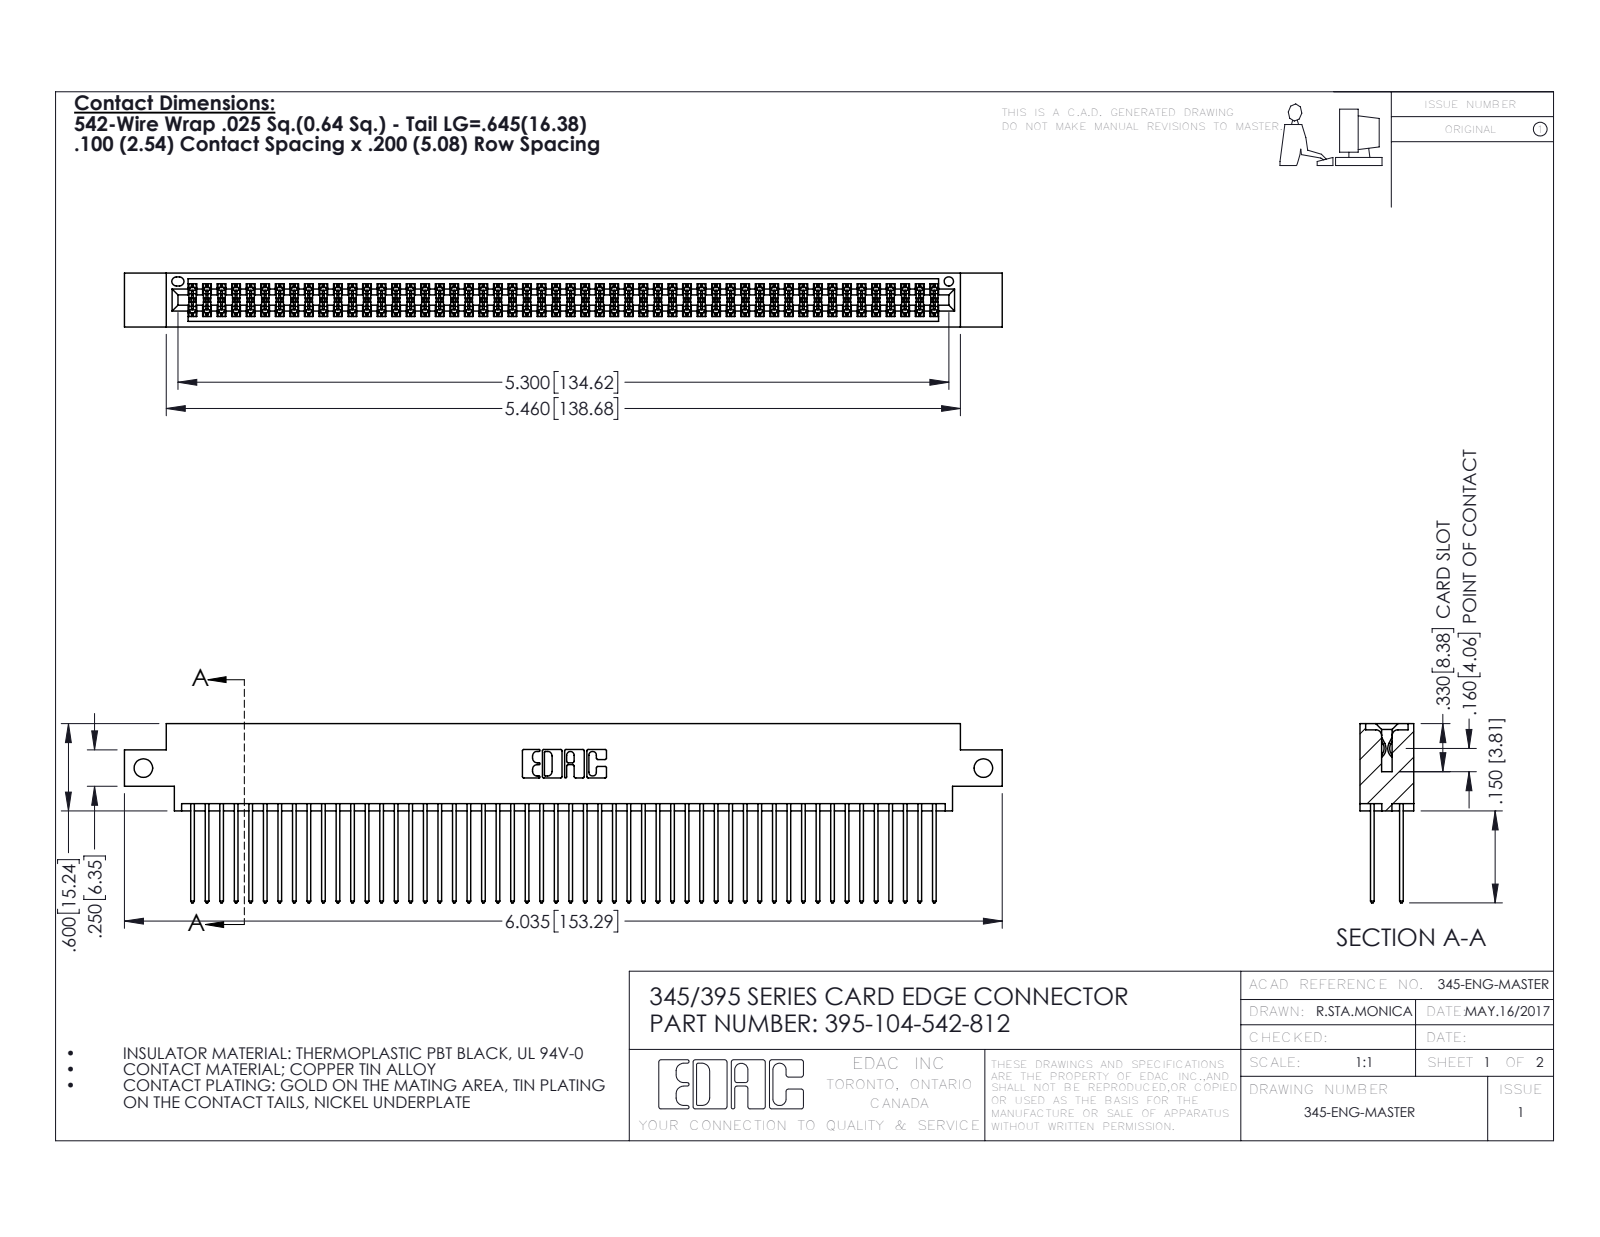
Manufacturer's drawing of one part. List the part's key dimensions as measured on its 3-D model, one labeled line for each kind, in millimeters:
Part name (STEP PRODUCT): 395-104-542-812; 345-292-001_345-293-142; 345 Part_0.170 Offset - Side Mount
STEP written by: SolidWorks 2016 (CONFIG_CONTROL_DESIGN)
Units: millimetres
Bodies: 105 solids, 5330 faces (3516 planar, 1814 cylindrical, 0 other)
Overall size (bounding box): 153.3 × 31.3 × 9.4
Volume: 15 300 mm³ · Surface area: 25 030 mm²
Round holes (diameter × count): ⌀3.3 ×2, ⌀1.6 ×1
Partial cylindrical surfaces — rounded edges, fillets, slot ends (radius × count): R0.2 ×156, R0.3 ×104, R0.3 ×22, R0.2 ×6, R0.8 ×6, R0.7 ×3, R0.4 ×2, R0.5 ×2
Main face-to-face distances: 7.6, 1.8, 5.1, 2.5, 6.9, 0.6, 9.4, 5.7, 4.4, 3.8
Hole centre spacings: 146.7
